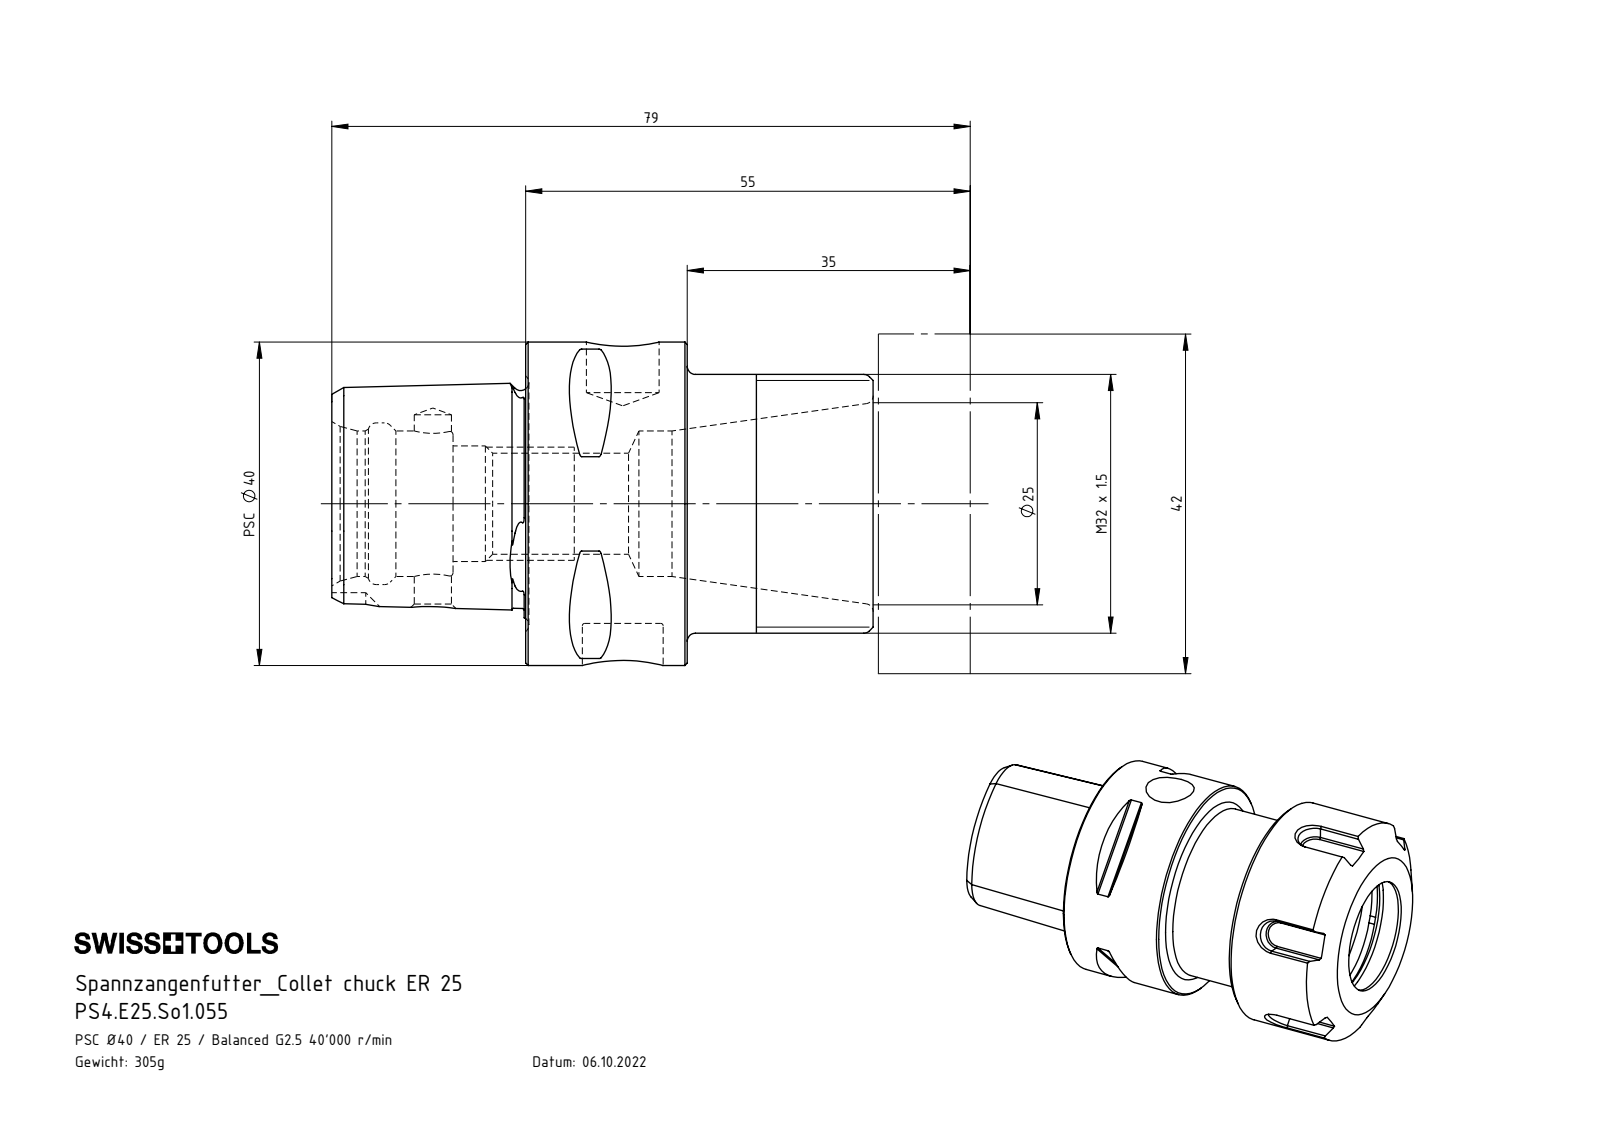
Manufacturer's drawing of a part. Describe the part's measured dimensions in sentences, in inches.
The part is named "PS4-E25.So1.055_A_Fertigbearbeitung; E25-ER1.001.020; PS4.E25.So1.055". Its 3-D file was written by "SolidWorks 2022 (CONFIG_CONTROL_DESIGN)". It is 2 solids with 243 faces: 71 planar, 44 cylindrical and 128 other. Overall it measures 3.11 by 1.642 by 1.642 inches. Its volume is 3.102 cubic inches and its surface area 29.72 square inches. Round holes: 1 of diameter 0.181, 1 of diameter 0.354, 1 of diameter 0.394, 1 of diameter 0.492, 1 of diameter 0.563, 1 of diameter 0.709, 1 of diameter 0.787, 1 of diameter 0.823, 1 of diameter 1.201, 1 of diameter 1.28. Round bosses or shafts: 1 of diameter 1.642, 1 of diameter 1.575, 1 of diameter 1.26. Partial cylindrical surfaces (rounded edges, fillets, slot ends): 8 of radius 0.012, 2 of radius 0.479, 1 of radius 0.157. The main face-to-face distances are 1.378, 0.787, 0.591, 2.165, 1.896, 1.108, 0.518, 0.27, 1.732, 1.693. The hole center spacings are 0.925.
